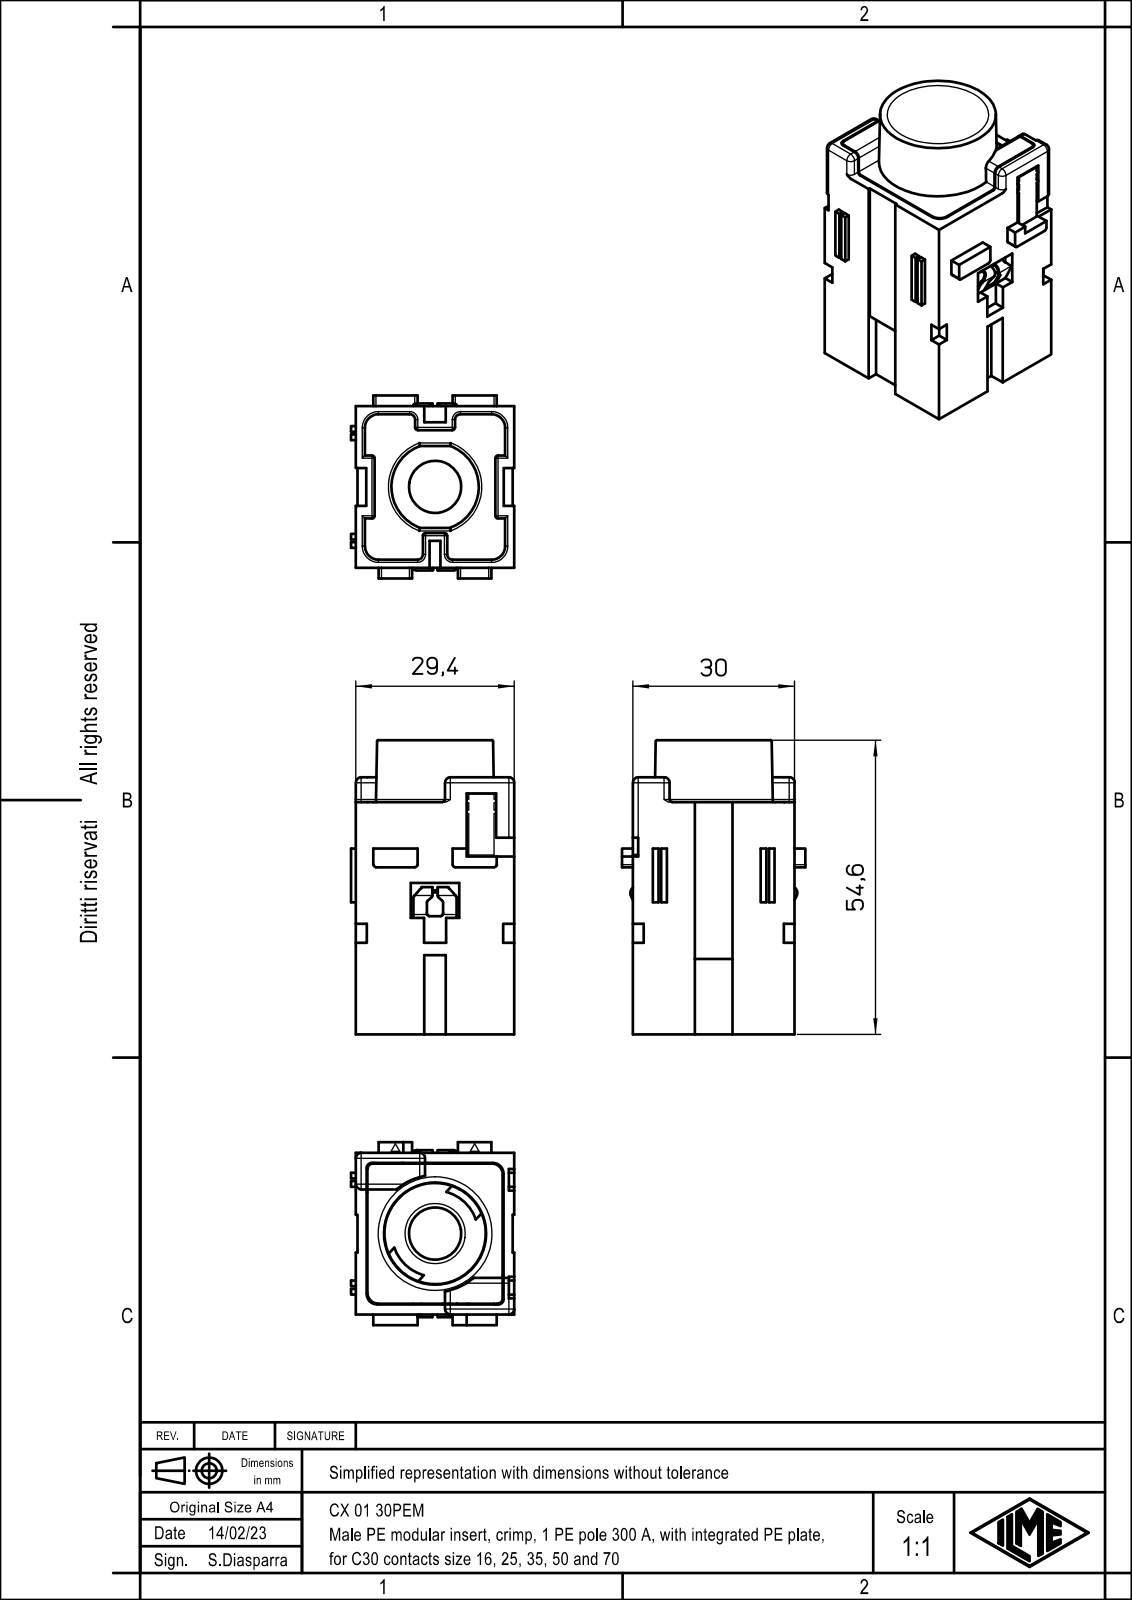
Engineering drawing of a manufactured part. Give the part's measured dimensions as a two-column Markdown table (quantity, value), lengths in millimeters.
| quantity | value |
| --- | --- |
| part name | CX 01 30PEM |
| STEP written by | Creo Elements/Direct Modeling 20.1B 02-Apr-2019 (C) Parametric Technology GmbH (AUTOMOTIVE_DESIGN) |
| units | millimeters |
| bodies | 1 solid, 450 faces (255 planar, 129 cylindrical, 66 other) |
| overall size | 54.6 × 34 × 30.3 |
| volume | 22 365 mm³ |
| surface area | 17 841 mm² |
| round holes (diameter × count) | 9.7 × 1, 18.8 × 1 |
| partial cylindrical surfaces (radius × count) | 0.5 × 54, 1 × 21, 0.35 × 8, 0.8 × 4, 1.1 × 4, 2.5 × 4, 2 × 2, 8 × 1 |
| main face-to-face distances | 2, 1.85, 27.4, 2.15, 27.25, 25.25, 30, 28, 28.15, 26.15 |
